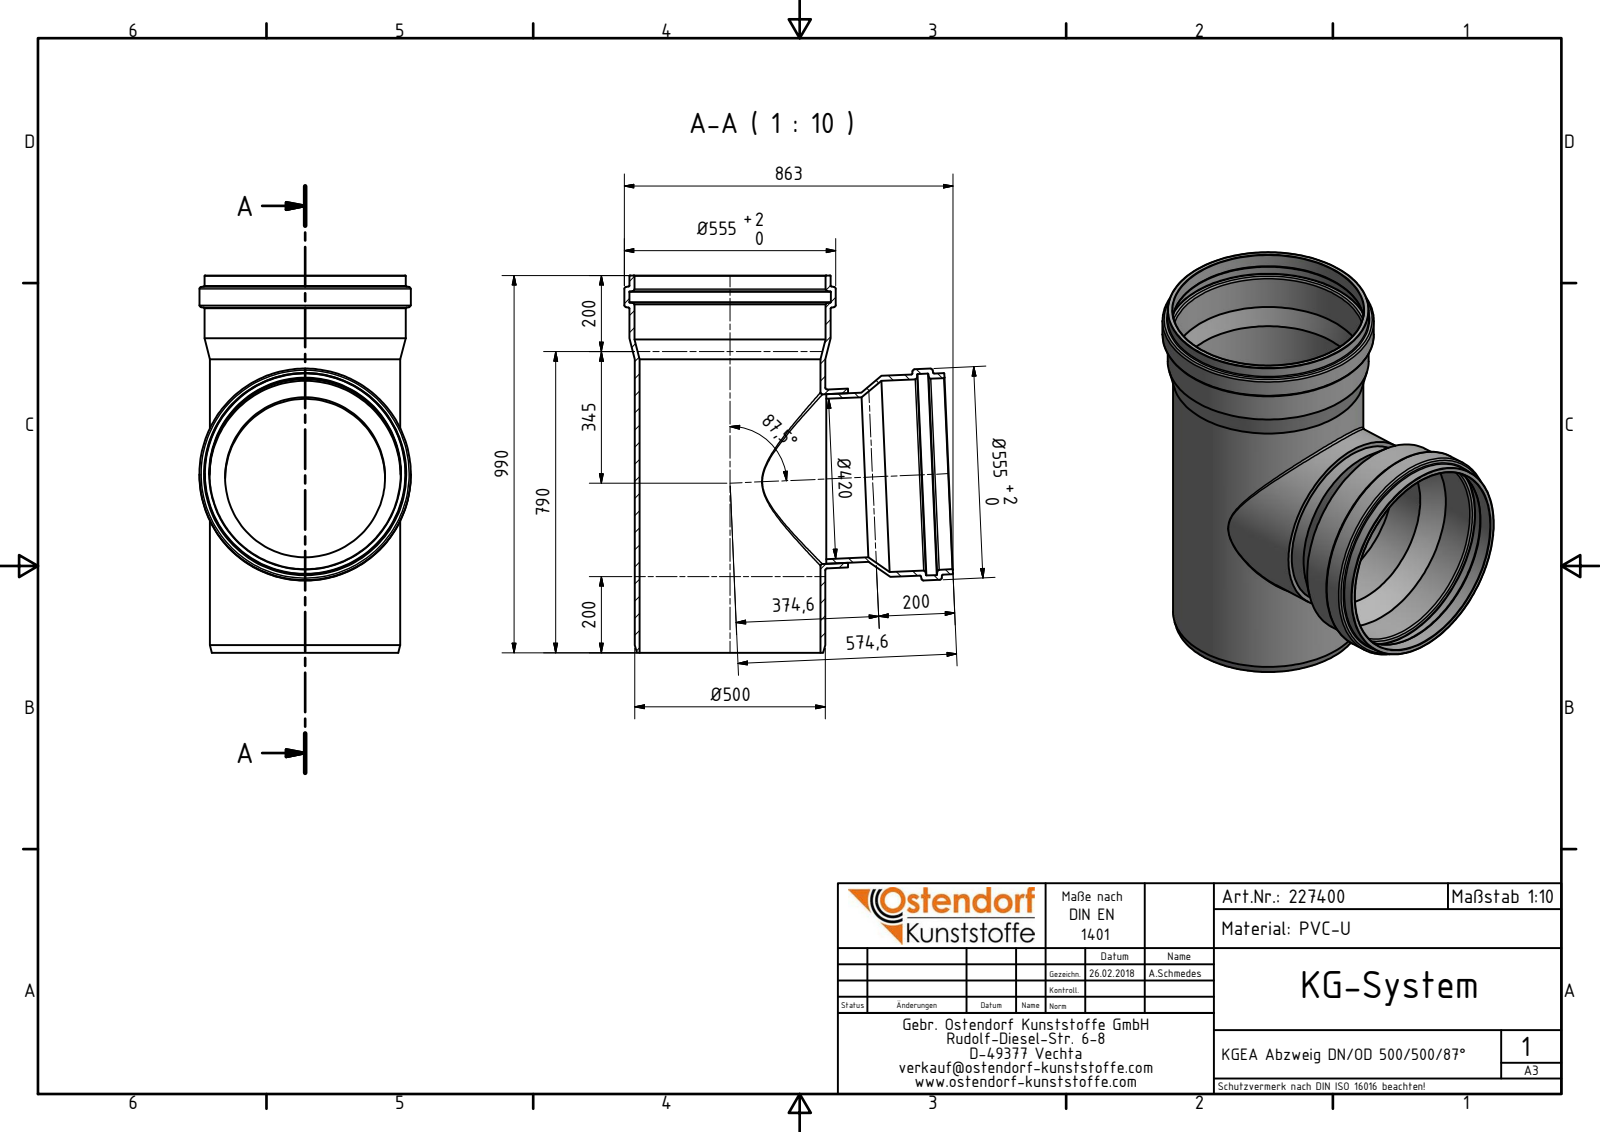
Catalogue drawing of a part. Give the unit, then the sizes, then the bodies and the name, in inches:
Units: inches
Overall size (bounding box): 38.976 × 33.976 × 21.85
Round holes (diameter × count): ⌀19.764 ×3, ⌀20.827 ×2, ⌀16.535 ×1, ⌀17.504 ×1, ⌀18.717 ×1
Round bosses / shafts (diameter × count): ⌀20.787 ×3, ⌀21.85 ×2, ⌀19.685 ×1, ⌀18.472 ×1, ⌀17.504 ×1
Main face-to-face distances: 2.259, 38.976
Volume: 1 601 in³ · Surface area: 6 684 in²
Bodies: 2 solids, 58 faces (5 planar, 18 cylindrical, 35 other)
Part name (STEP PRODUCT): 227400 KGEA Abzweig DN_OD 500_500_87°; 227400 KGEA Abzweig DN_OD 500_500_87° Abzweig
STEP written by: Autodesk Inventor 2016 (AUTOMOTIVE_DESIGN)
